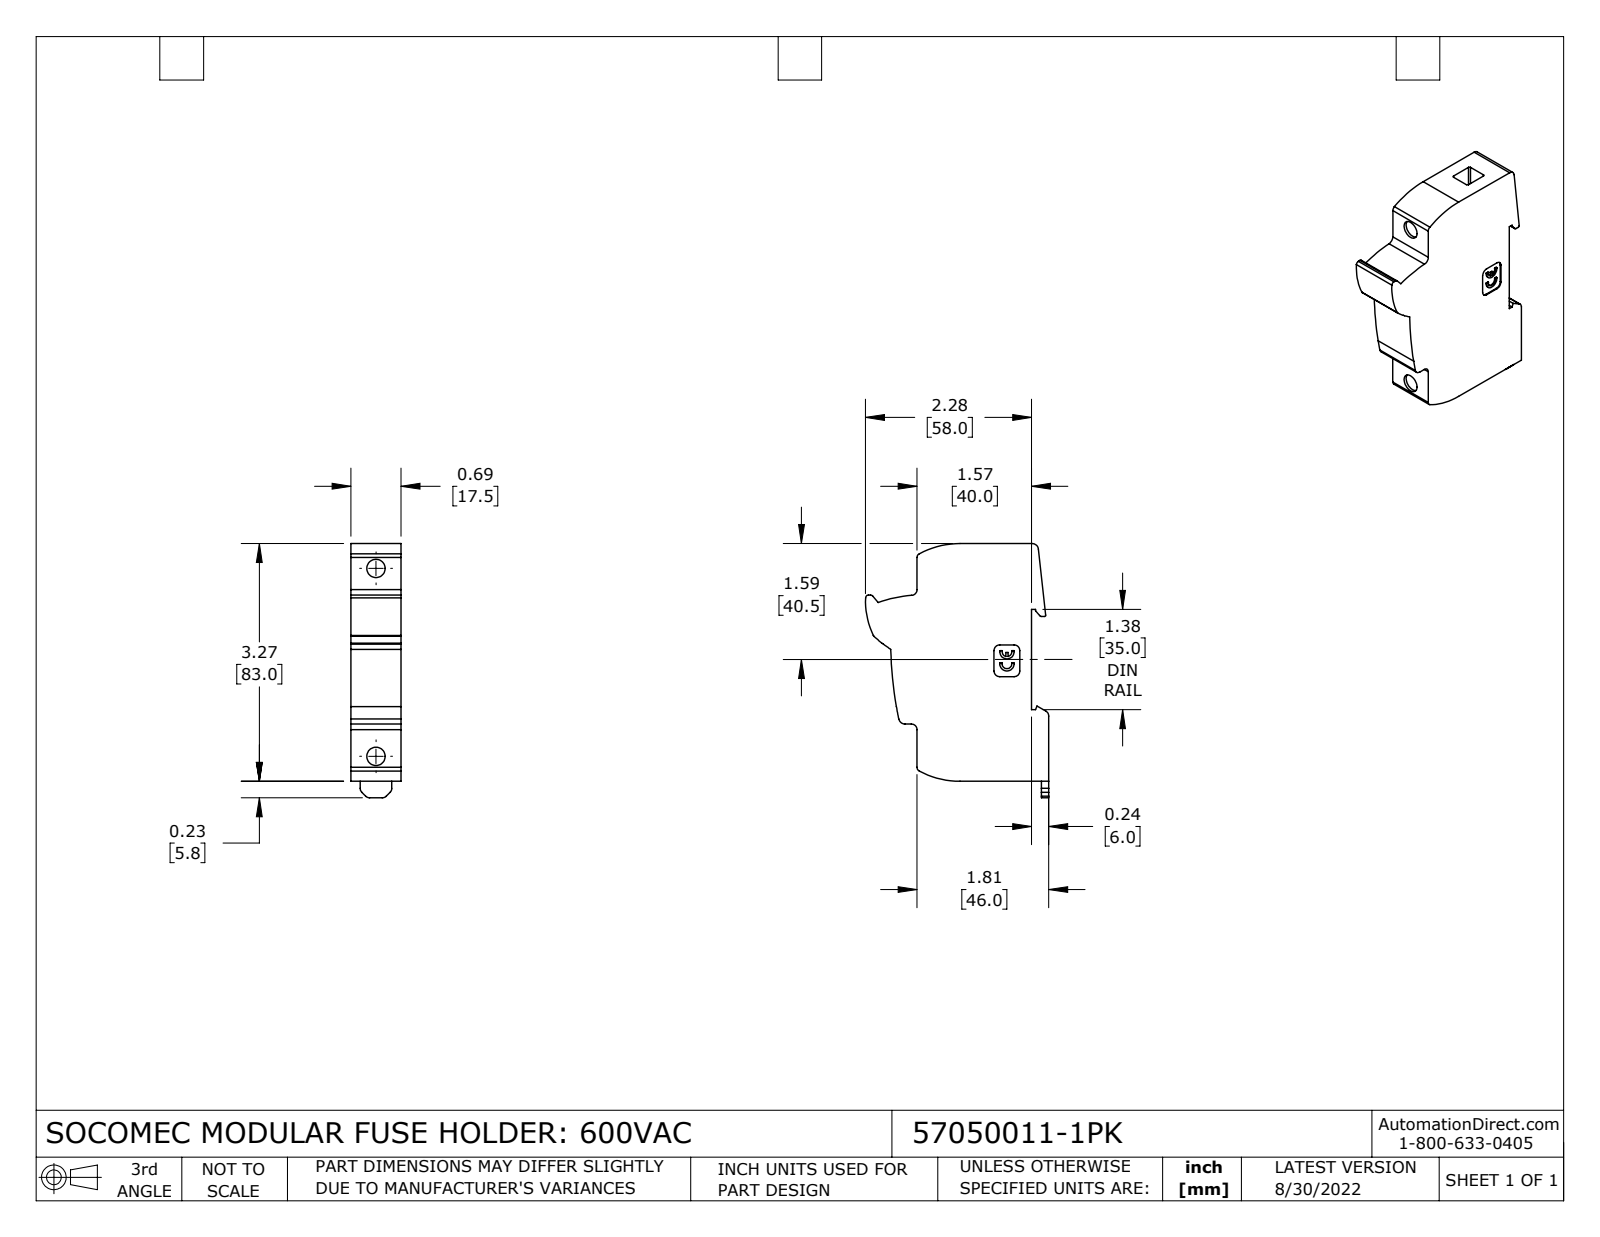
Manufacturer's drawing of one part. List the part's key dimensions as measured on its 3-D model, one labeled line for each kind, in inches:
Part name (STEP PRODUCT): 57050011-1PK
STEP written by: SolidWorks 2021 (CONFIG_CONTROL_DESIGN)
Units: inches
Bodies: 1 solid, 105 faces (52 planar, 53 cylindrical, 0 other)
Overall size (bounding box): 3.496 × 2.52 × 0.689
Volume: 4.229 in³ · Surface area: 21.33 in²
Round holes (diameter × count): ⌀0.252 ×2
Partial cylindrical surfaces — rounded edges, fillets, slot ends (radius × count): R0.079 ×11, R0.02 ×5, R0.039 ×4, R0.059 ×2, R0.067 ×2, R0.087 ×2, R0.098 ×2, R1.186 ×2
Main face-to-face distances: 0.689, 0.236, 1.575, 3.268, 1.811, 0.199, 0.49, 0.291, 0.518, 0.281
Hole centre spacings: 2.583
